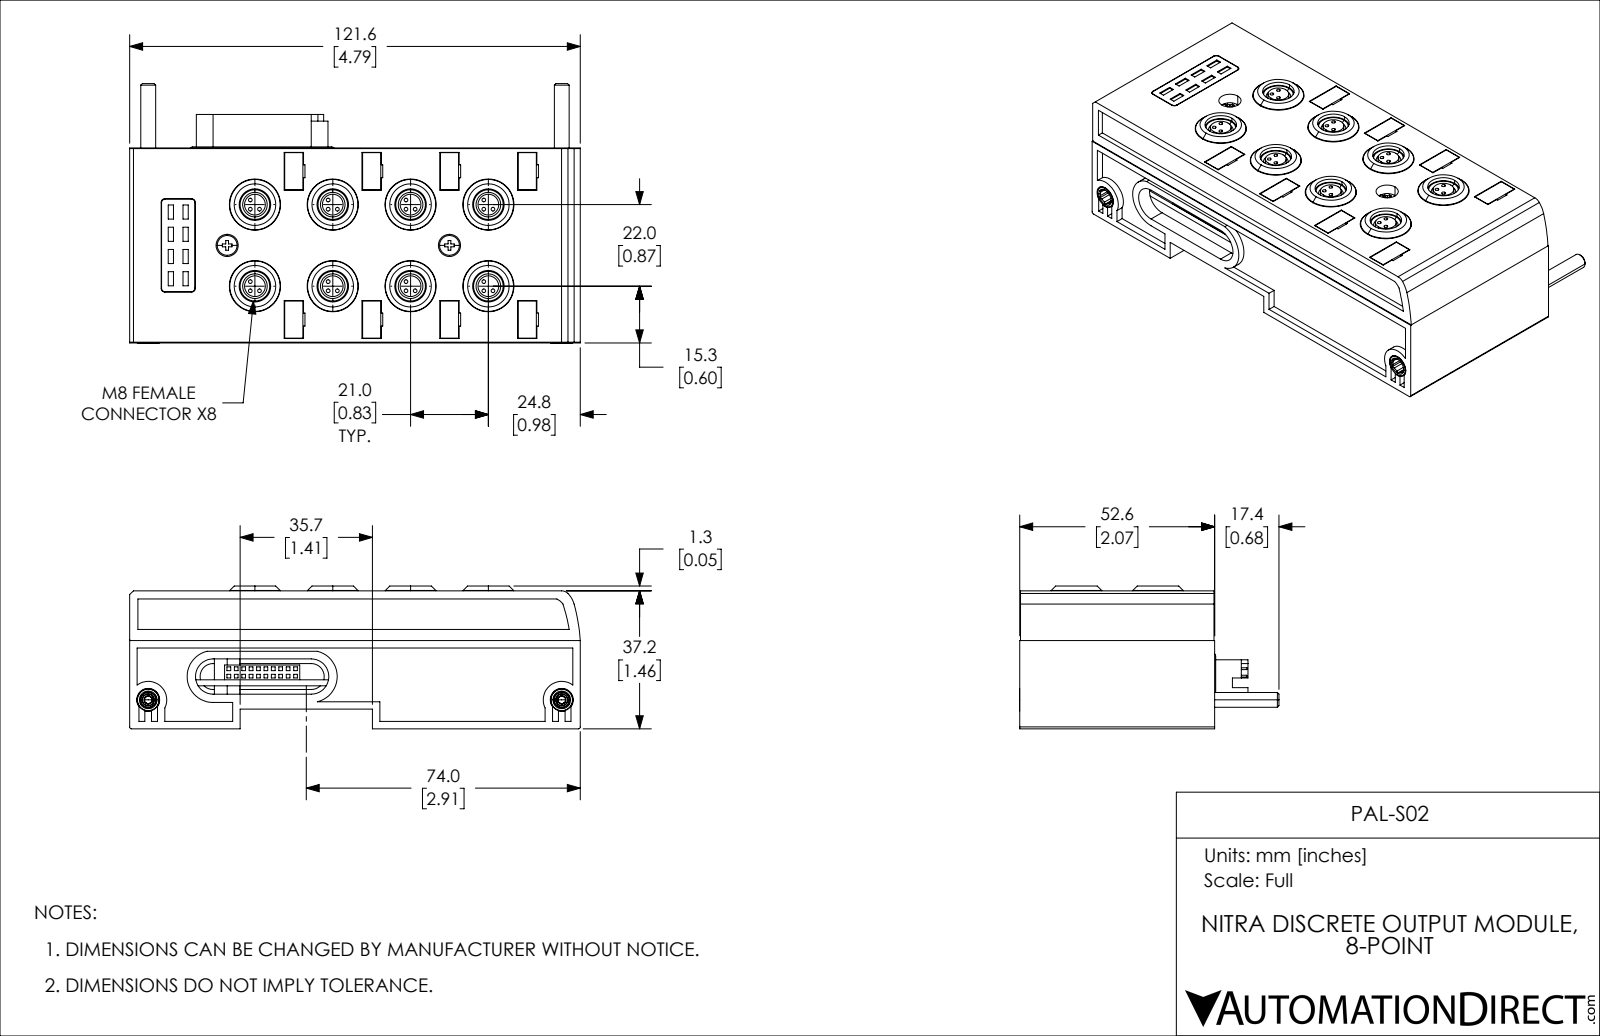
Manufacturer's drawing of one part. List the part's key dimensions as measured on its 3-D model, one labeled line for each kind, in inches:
Part name (STEP PRODUCT): PAL-S02
STEP written by: SolidWorks 2019 (CONFIG_CONTROL_DESIGN)
Units: inches
Bodies: 5 solids, 1010 faces (676 planar, 224 cylindrical, 110 other)
Overall size (bounding box): 4.787 × 2.756 × 1.516
Volume: 8.884 in³ · Surface area: 99.88 in²
Round holes (diameter × count): ⌀0.039 ×24, ⌀0.262 ×8, ⌀0.335 ×8, ⌀0.543 ×8, ⌀0.128 ×2, ⌀0.236 ×2, ⌀0.244 ×2
Round bosses / shafts (diameter × count): ⌀0.535 ×8, ⌀0.22 ×8, ⌀0.272 ×2, ⌀0.236 ×2, ⌀0.211 ×2, ⌀0.157 ×2
Partial cylindrical surfaces — rounded edges, fillets, slot ends (radius × count): R0.039 ×8, R0.02 ×2, R0.034 ×2, R0.079 ×2, R0.082 ×2, R0.138 ×2, R0.177 ×2, R0.187 ×2
Main face-to-face distances: 0.315, 0.528, 0.063, 0.52, 0.937, 1.465, 0.622, 1.15, 0.417, 0.205
Hole centre spacings: 0.069, 0.827, 1.197, 0.78, 0.877, 0.098, 0.866, 1.654
